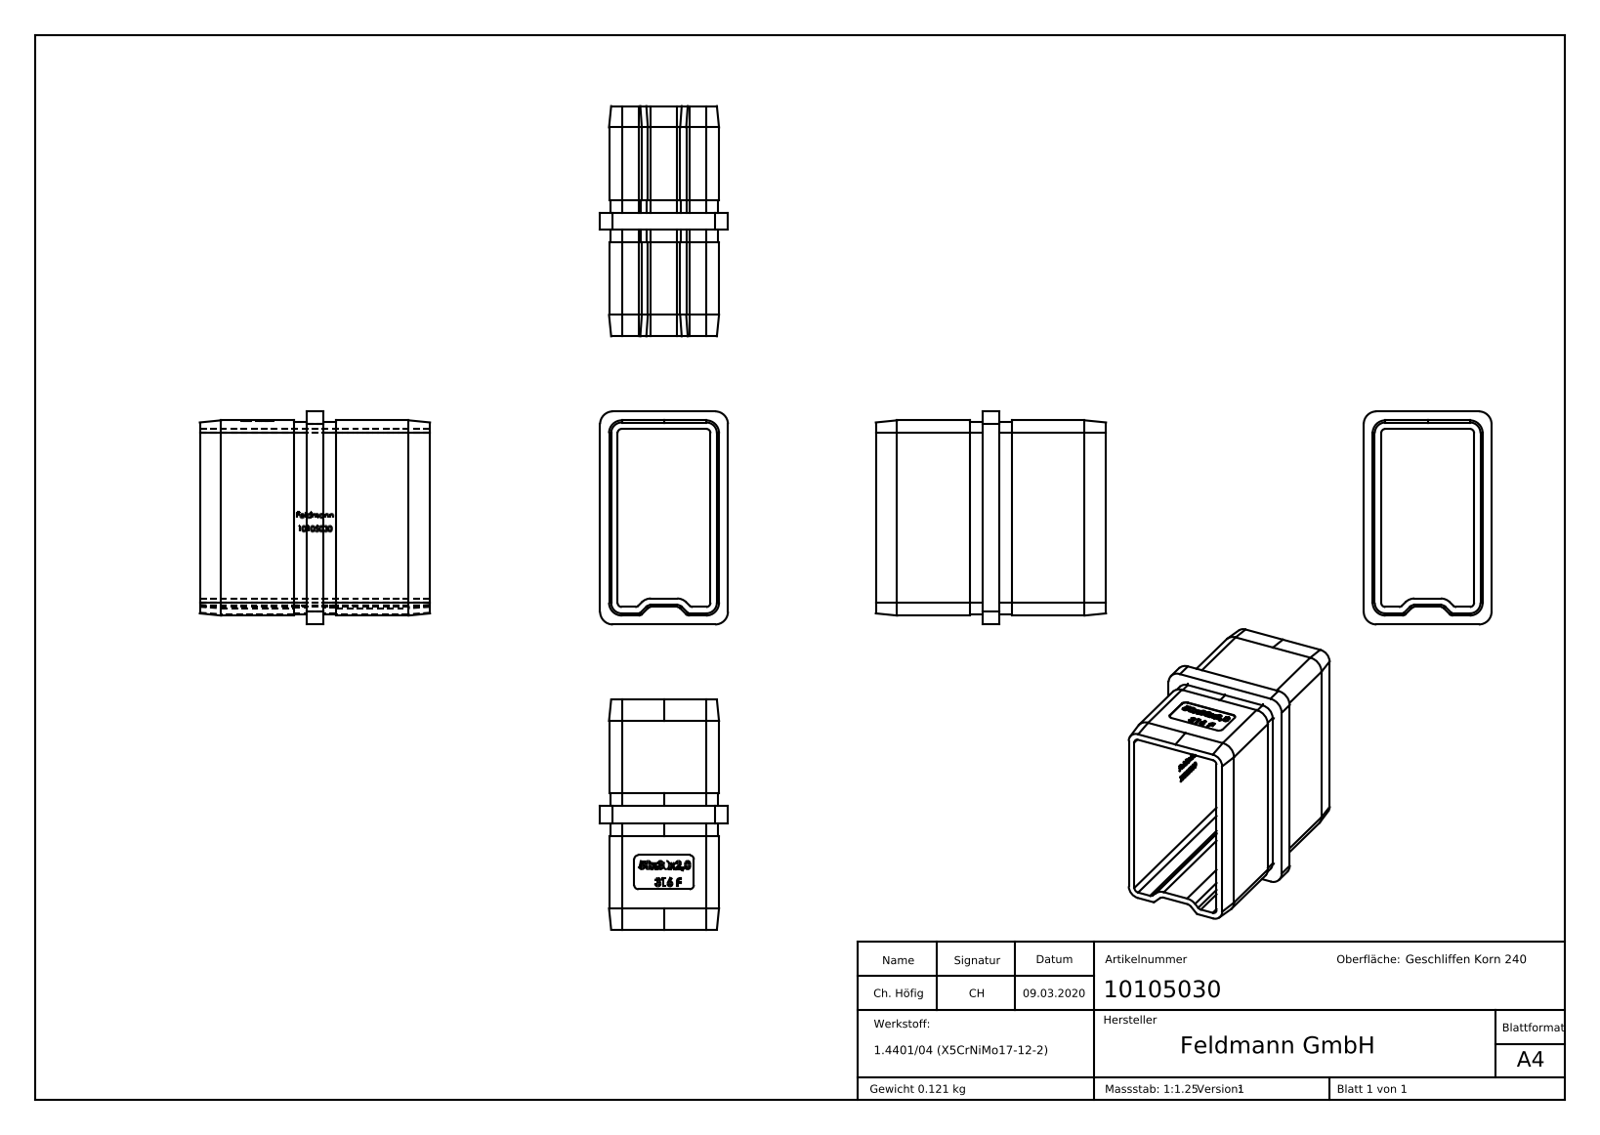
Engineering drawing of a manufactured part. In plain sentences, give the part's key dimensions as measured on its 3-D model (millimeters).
The part is named "10105030". Its 3-D file was written by "SolidWorks 2015 (CONFIG_CONTROL_DESIGN)". It is 1 solid with 539 faces: 289 planar, 48 cylindrical and 202 other. Overall it measures 54 by 50 by 30 millimeters. Its volume is 15 128 cubic millimeters and its surface area 15 680 square millimeters. Partial cylindrical surfaces (rounded edges, fillets, slot ends): 14 of radius 1, 10 of radius 3, 4 of radius 2.7, 2 of radius 0.7, 2 of radius 1.3. The main face-to-face distances are 2, 23.8, 21.8, 25.8, 41.8, 43.8, 1.7, 4, 4.1, 2.1.
